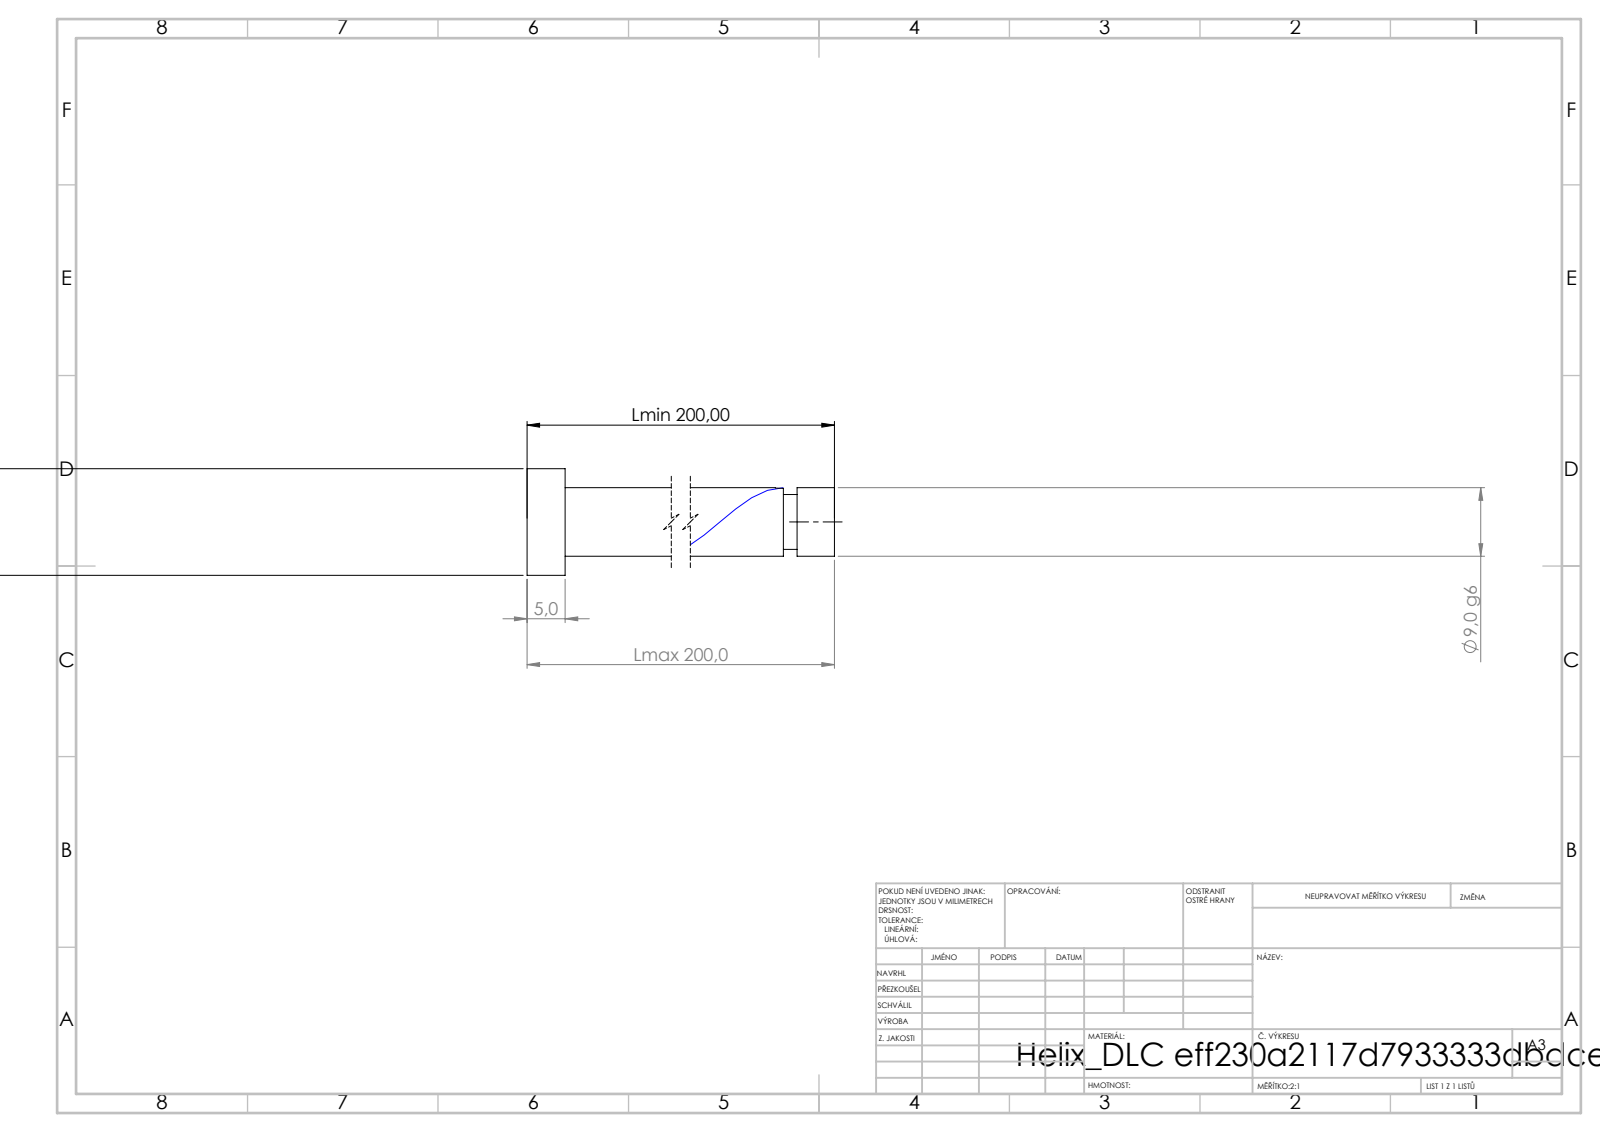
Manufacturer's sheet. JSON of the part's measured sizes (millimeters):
{"step_written_by": "SolidWorks 2019 (CONFIG_CONTROL_DESIGN)", "units": "millimeters", "bodies": {"solids": 1, "faces": 21, "planar": 6, "cylindrical": 14, "other": 1}, "overall_size": [200, 14, 14], "volume_mm3": 13012, "surface_area_mm2": 6201, "round_bosses_or_shafts": [[14, 1], [9, 1], [7.2, 1]], "face_to_face_distances": [5, 200, 195, 195.1, 190.1, 4.9, 193.3, 188.3, 1.8, 6.7]}
